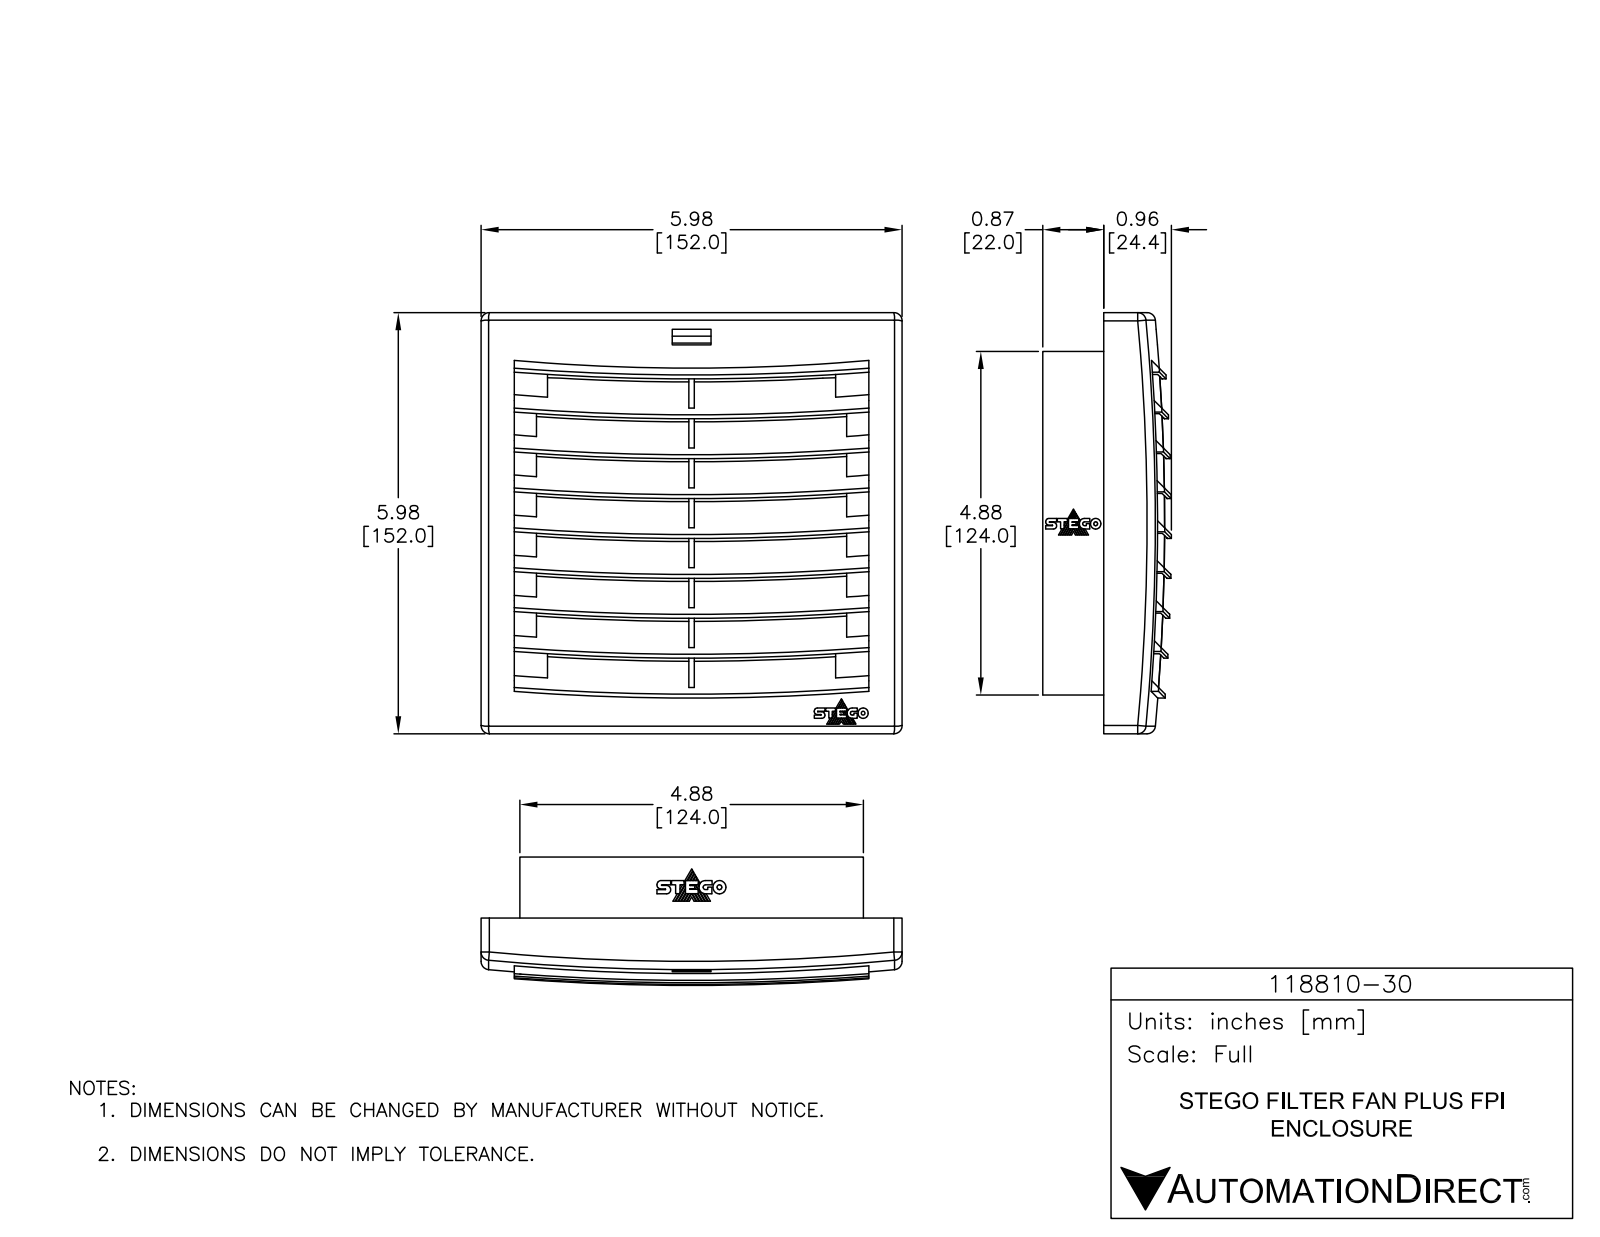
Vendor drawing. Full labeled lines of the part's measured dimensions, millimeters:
Part name (STEP PRODUCT): 118810-30
STEP written by: SolidWorks 2018 (AUTOMOTIVE_DESIGN)
Units: millimetres
Bodies: 1 solid, 323 faces (175 planar, 148 cylindrical, 0 other)
Overall size (bounding box): 152 × 152 × 47
Volume: 358 200 mm³ · Surface area: 147 700 mm²
Round holes (diameter × count): ⌀82.6 ×1, ⌀105.4 ×1
Round bosses / shafts (diameter × count): ⌀88.6 ×1, ⌀68.9 ×1
Partial cylindrical surfaces — rounded edges, fillets, slot ends (radius × count): R349.4 ×16, R3 ×4, R13.2 ×1, R21.6 ×1, R24.6 ×1, R31.4 ×1, R293.8 ×1
Main face-to-face distances: 10.8, 1.5, 21.6, 6.6, 12.3, 9.3, 17.1, 134.9, 54.1, 43.3
